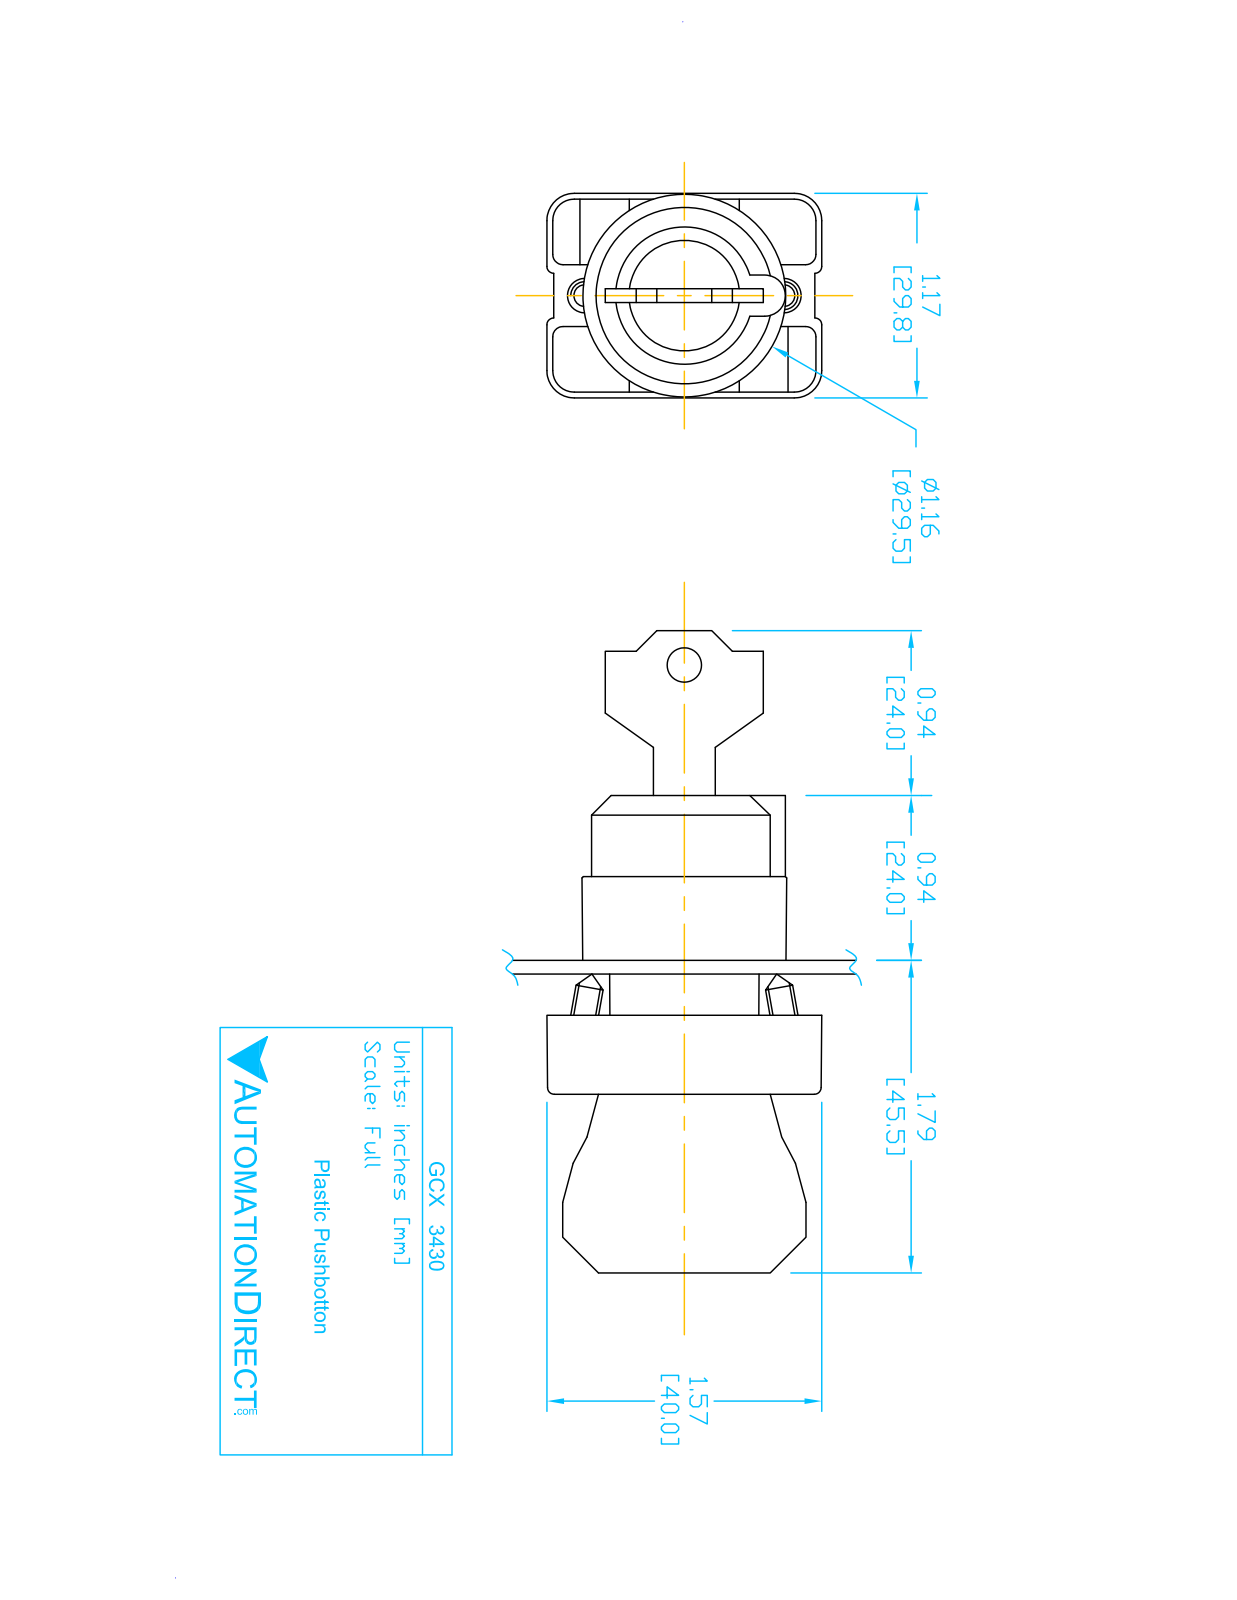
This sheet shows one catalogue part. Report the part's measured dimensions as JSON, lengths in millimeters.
{"part_name": "ECX3029-2; ecx1040; GCX3430 OPERATOR; GCX3430", "step_written_by": "SolidWorks 2016 (AUTOMOTIVE_DESIGN)", "units": "millimeters", "bodies": {"solids": 7, "faces": 405, "planar": 235, "cylindrical": 142, "other": 28}, "overall_size": [67.3, 40.2, 29.9], "volume_mm3": 32890, "surface_area_mm2": 20830, "round_holes": [[2, 2], [3.1, 2], [3.3, 2], [2.2, 1], [5, 1], [15, 1], [22.3, 1], [22.6, 1], [26, 1]], "round_bosses_or_shafts": [[4, 2], [29.8, 1], [25.5, 1], [24.5, 1], [24, 1], [21.7, 1], [19.8, 1], [14.5, 1]], "partial_cylinders_radius": [[1.5, 24], [1, 12], [3.1, 12], [4, 12], [1, 6], [3.3, 2], [0.5, 1], [1.6, 1]], "face_to_face_distances": [18.3, 14.7, 0.8, 0.8, 17.5, 15.2, 13.7, 16.2, 14.7, 3.1], "hole_center_spacings": [6, 13.8, 12, 12.4]}
